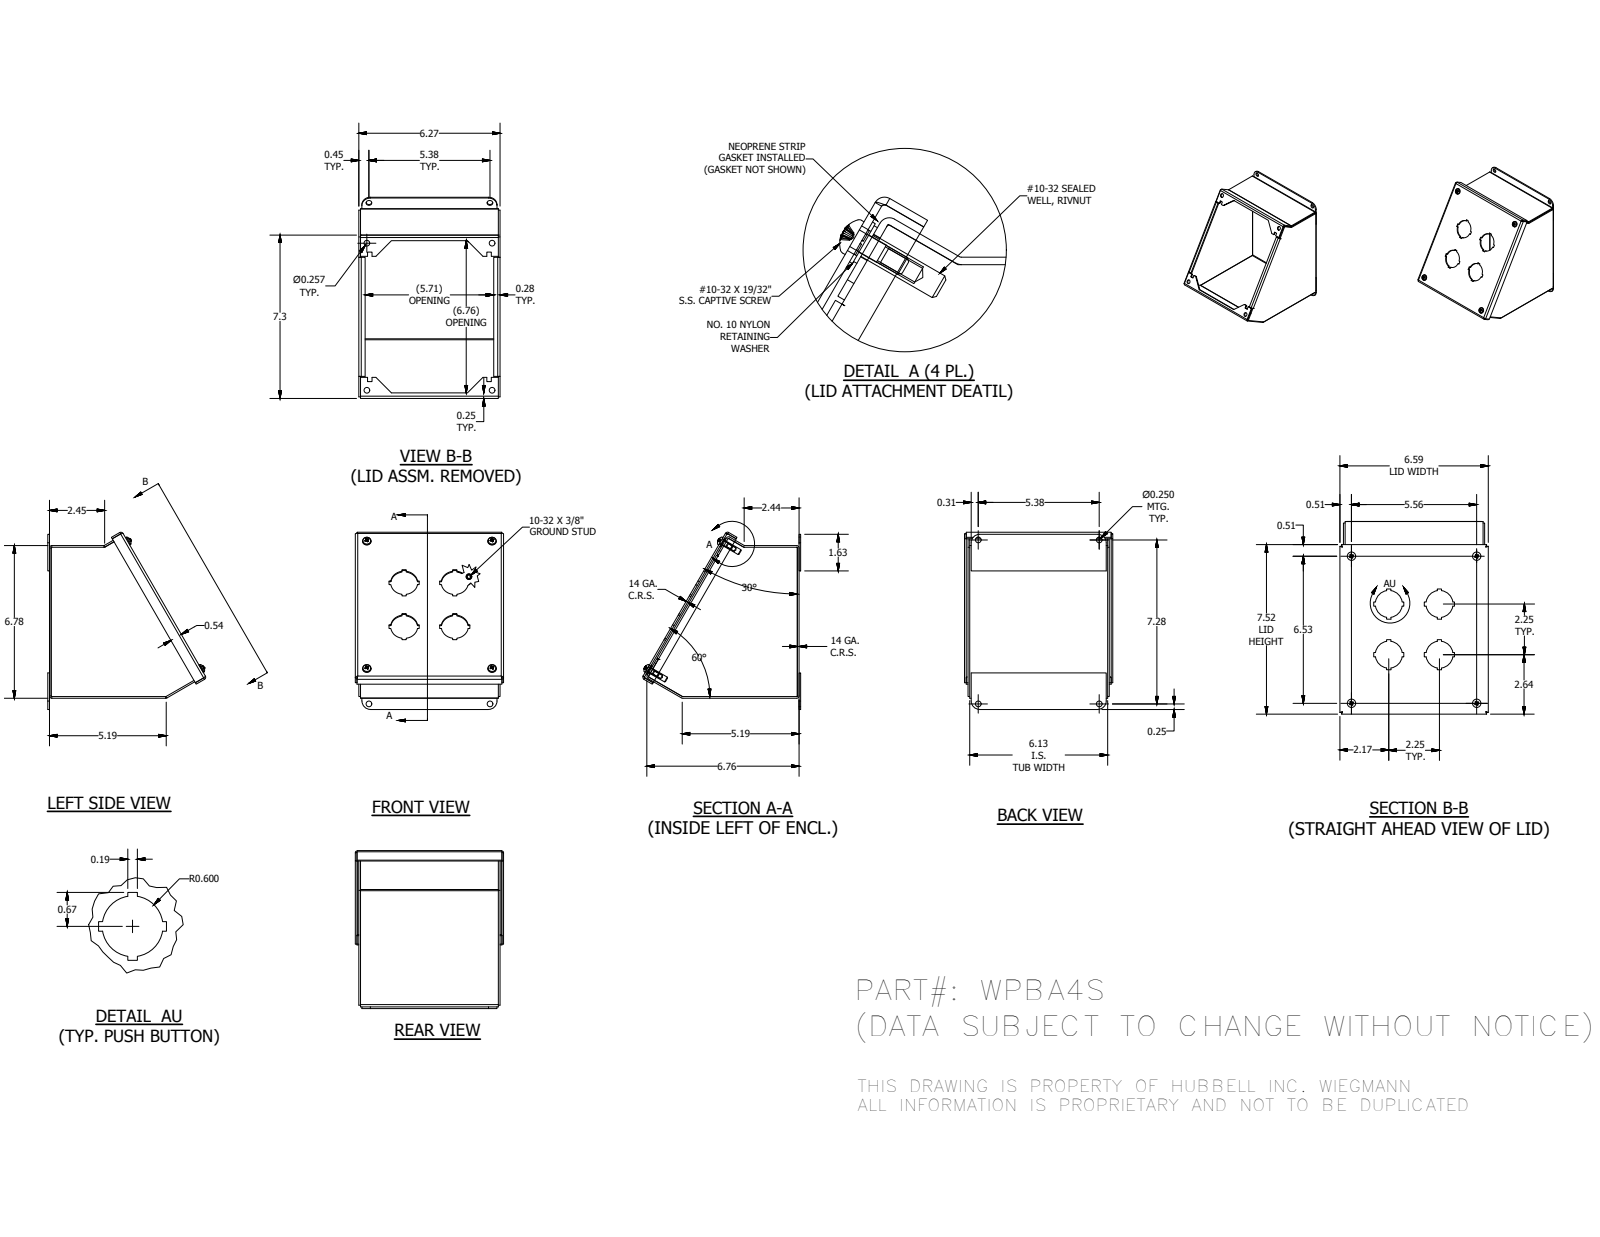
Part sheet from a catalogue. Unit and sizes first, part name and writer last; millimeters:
Units: millimetres
Overall size (bounding box): 199.98 × 178.2 × 167.31
Round holes (diameter × count): ⌀3.96 ×4, ⌀4.98 ×4, ⌀6.35 ×4, ⌀6.53 ×4, ⌀7.06 ×4, ⌀7.14 ×4, ⌀30.48 ×4
Round bosses / shafts (diameter × count): ⌀4.83 ×5, ⌀11.51 ×4, ⌀10.31 ×4, ⌀9.47 ×4, ⌀6.3 ×4, ⌀6.35 ×1
Partial cylindrical surfaces — rounded edges, fillets, slot ends (radius × count): R0.79 ×12, R2.67 ×12, R2.27 ×4, R9.53 ×4
Main face-to-face distances: 1.88, 157.45, 155.57, 159.33, 170.33, 3.76, 168.45, 172.21, 3.66, 3.98
Hole centre spacings: 68.42, 118.8, 141.27, 141.3, 165.07, 165.91, 0.84, 57.14
Volume: 311 895 mm³ · Surface area: 342 676 mm²
Bodies: 19 solids, 544 faces (339 planar, 106 cylindrical, 99 other)
Part name (STEP PRODUCT): WPBA4SBKP; WPBA2ROWEWPR; WPBA2ROWEWPL; 34984 (+6 more)
STEP written by: Autodesk Inventor 2014 (AUTOMOTIVE_DESIGN)
